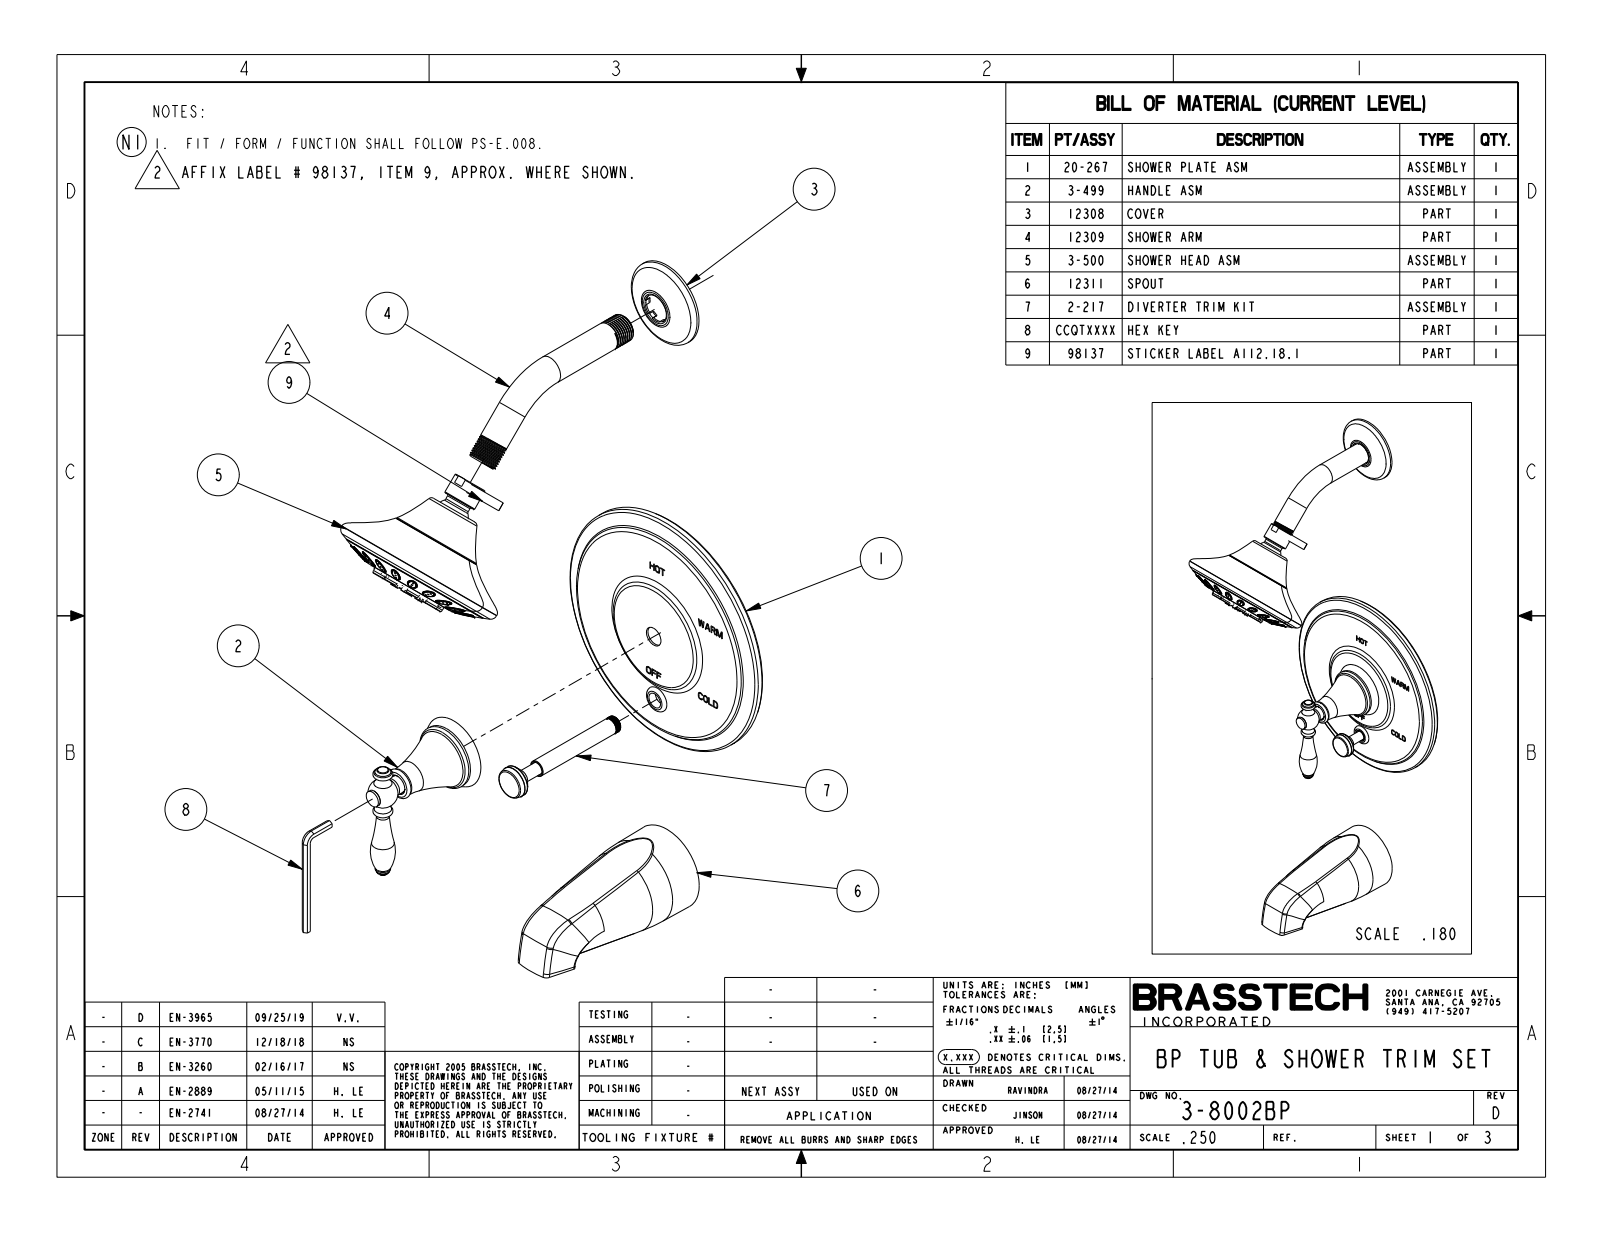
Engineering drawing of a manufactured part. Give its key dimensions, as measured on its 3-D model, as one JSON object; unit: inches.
{"part_name": "NCIP-028_1_AF0; PRT0010_1_AF0; 91033_1; 3-498_AF0_ASM (+8 more)", "step_written_by": "PRO/ENGINEER BY PARAMETRIC TECHNOLOGY CORPORATION, 2013150 (CONFIG_CONTROL_DESIGN)", "units": "inches", "bodies": {"solids": 28, "faces": 4539, "planar": 1267, "cylindrical": 1025, "other": 2247}, "overall_size": [21.51, 11.074, 7.283], "volume_in3": 17.14, "surface_area_in2": 472.2, "round_holes": [[0.079, 13], [0.063, 12], [0.118, 11], [0.213, 8], [0.268, 8], [0.37, 8], [0.236, 5], [0.685, 2], [0.15, 1], [0.156, 1], [0.181, 1], [0.197, 1]], "round_bosses_or_shafts": [[0.362, 8], [0.165, 8], [0.079, 8], [0.236, 5], [0.197, 5], [0.811, 2], [7.283, 1], [4.921, 1]], "partial_cylinders_radius": [[0.012, 52], [0.004, 30], [0.032, 20], [6.082, 20], [0.02, 18], [0.03, 18], [0.015, 15], [0.063, 14]], "face_to_face_distances": [0.059, 0.138, 0.197, 0.079, 0.453, 0.315, 0.374, 0.512, 0.394, 0.118], "hole_center_spacings": [0.984, 0.925, 1.673, 1.062, 0.377, 0.453, 0.985, 1.588]}
